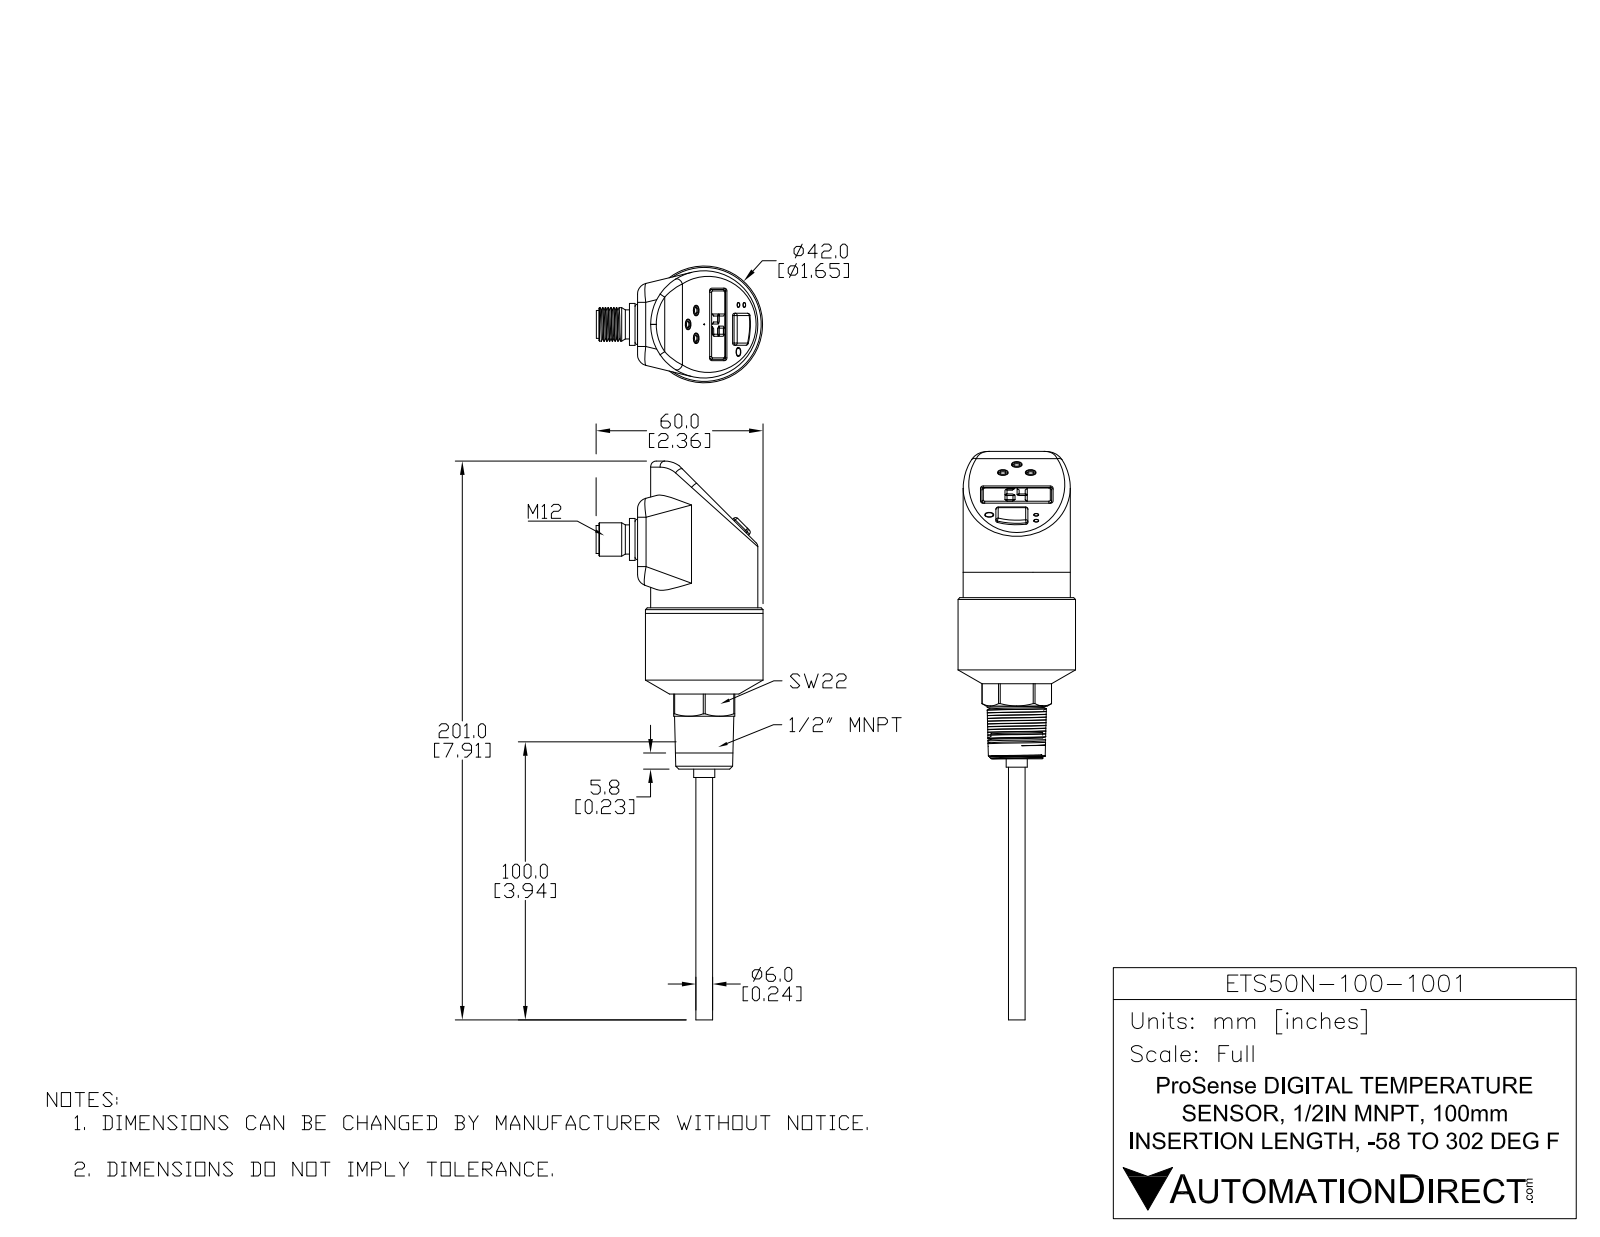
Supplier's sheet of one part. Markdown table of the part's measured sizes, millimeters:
| quantity | value |
| --- | --- |
| part name | ETS50N-100-1001 |
| STEP written by | SolidWorks 2016 (AUTOMOTIVE_DESIGN) |
| units | millimeters |
| bodies | 1 solid, 324 faces (138 planar, 95 cylindrical, 91 other) |
| overall size | 204.49 × 59.95 × 42.3 |
| volume | 109 158 mm³ |
| surface area | 19 661 mm² |
| round holes (diameter × count) | 8.45 × 1, 11 × 1 |
| round bosses / shafts (diameter × count) | 1.4 × 4, 1 × 4, 42.3 × 1, 38.55 × 1, 15.1 × 1, 14.56 × 1, 12 × 1, 10.5 × 1 |
| partial cylindrical surfaces (radius × count) | 1 × 8, 0.8 × 7, 0.5 × 4, 3.99 × 4, 7 × 4, 0.61 × 1, 2 × 1, 9.01 × 1 |
| main face-to-face distances | 22, 57.99, 13.9, 13, 0.9, 2, 2.9, 15.9, 37.9, 35 |
